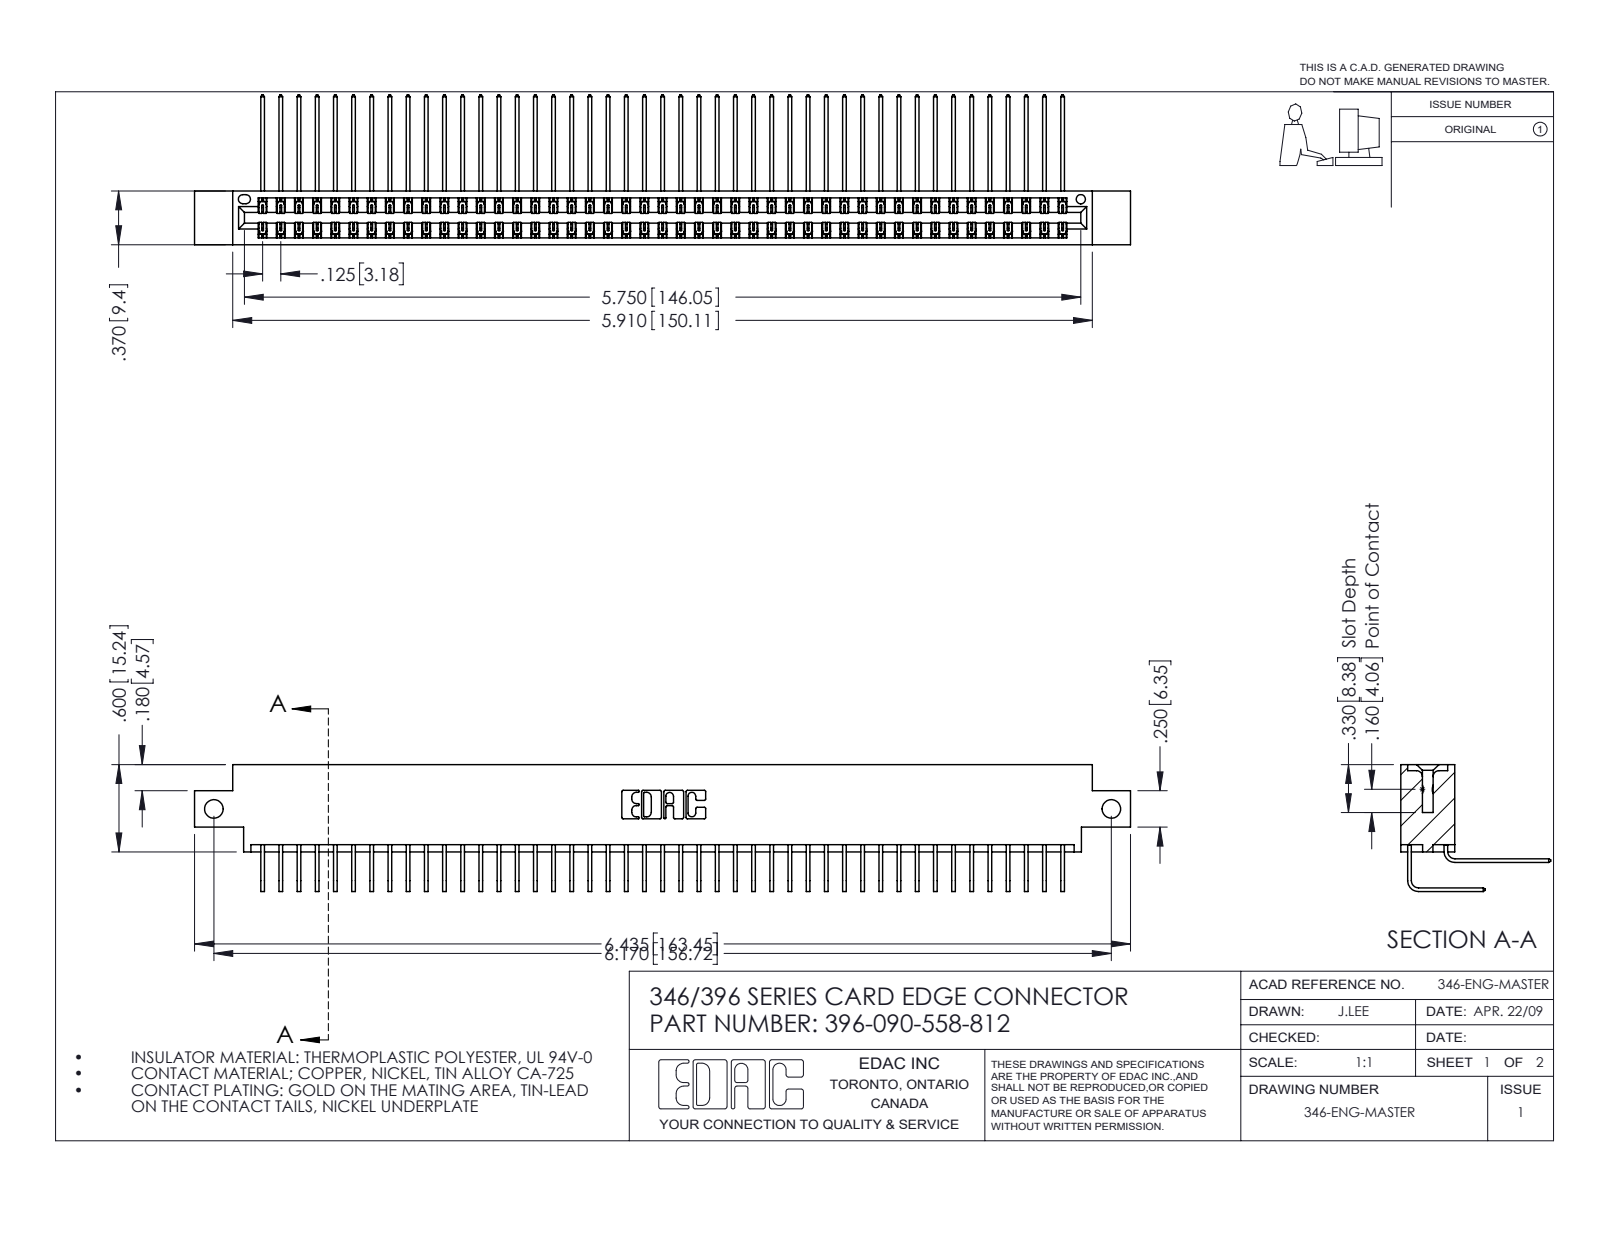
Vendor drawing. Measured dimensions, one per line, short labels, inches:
name: 345-292-001_558 Tail - 2; 345-292-001_558 559 Tail - 1; 396-090-558-812; 346 Part_0.170 Offset - Side Mount
written by: SolidWorks 2016 (CONFIG_CONTROL_DESIGN)
unit: in
bodies: 91 solids, 4986 faces (3410 planar, 1576 cylindrical, 0 other)
size: 6.435 × 1.03 × 0.873
volume: 0.991 in³; area: 38.6 in²
holes: 2× ⌀0.128, 1× ⌀0.064
rounds: 135× R0.006, 22× R0.01, 6× R0.007, 6× R0.031, 3× R0.026, 2× R0.014, 2× R0.022, 2× R0.024
face distances: 0.322, 0.048, 0.025, 0.37, 0.25, 0.298, 0.072, 0.275, 0.148, 0.222
hole spacings: 6.17
